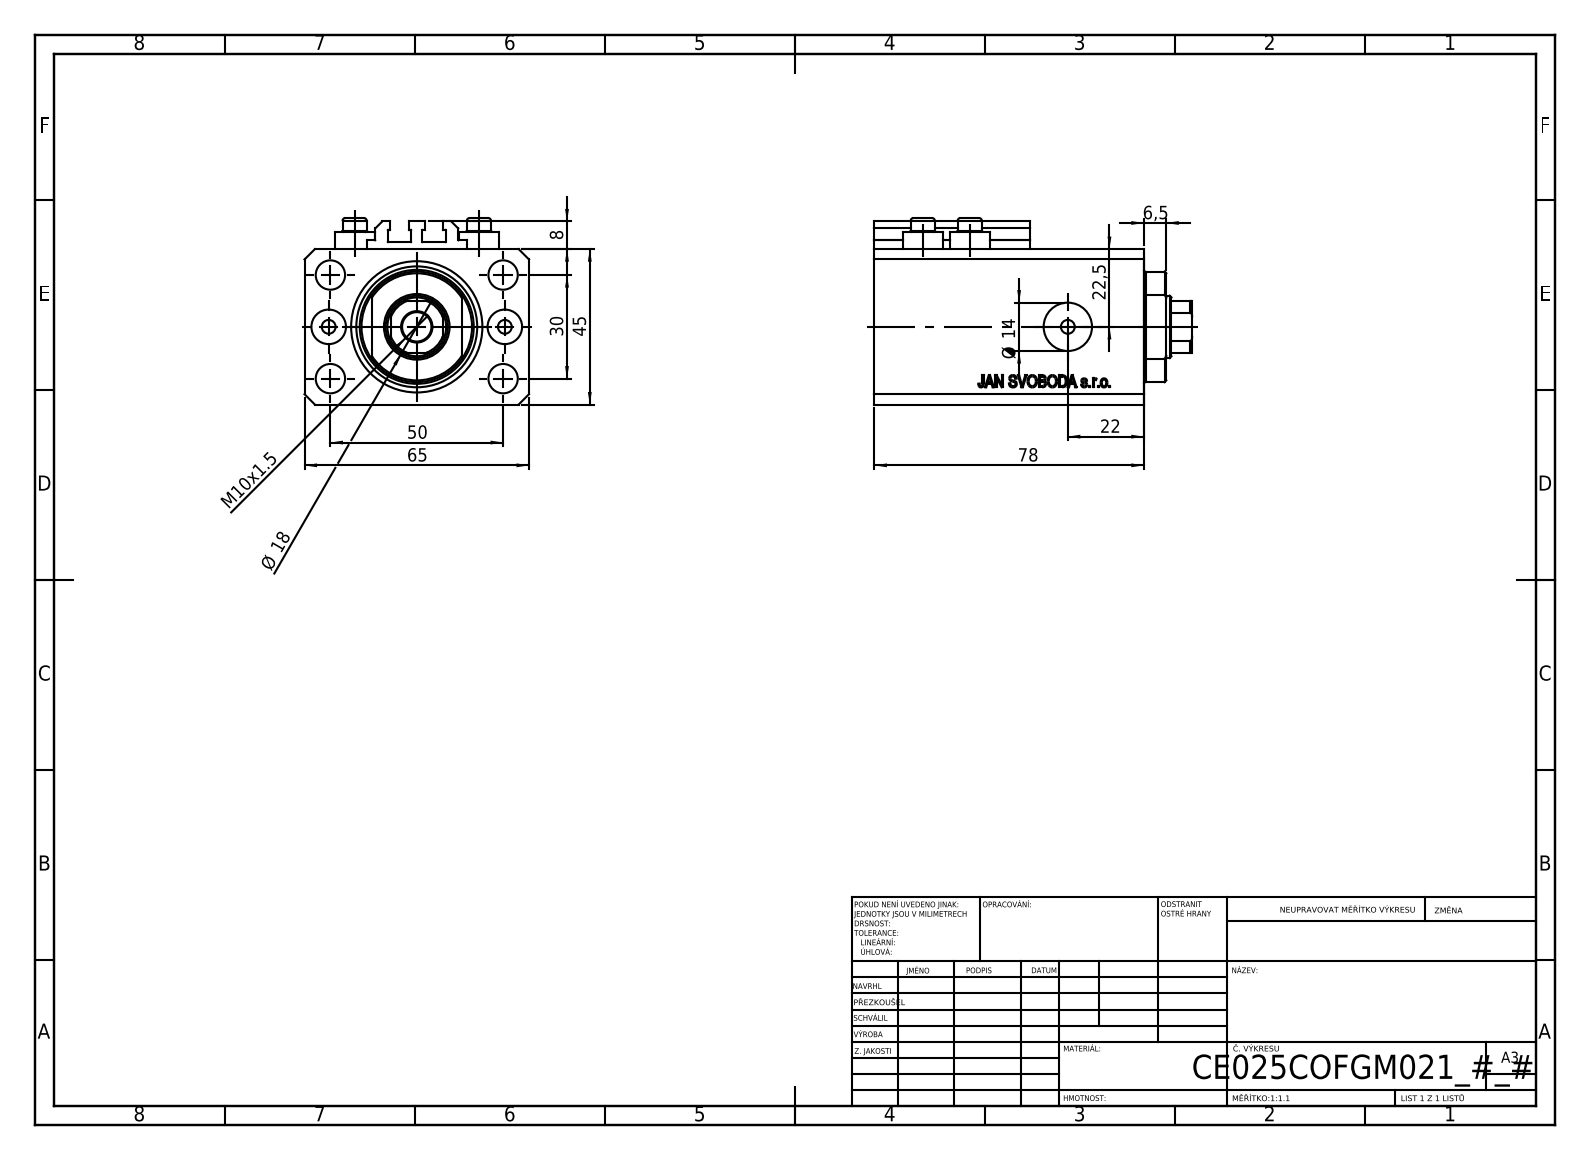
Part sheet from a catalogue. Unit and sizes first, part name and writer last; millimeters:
Units: millimetres
Overall size (bounding box): 92 × 65 × 54
Round holes (diameter × count): ⌀4 ×8, ⌀8.5 ×5, ⌀10 ×2, ⌀14 ×2, ⌀18 ×1, ⌀25 ×1, ⌀38 ×1
Round bosses / shafts (diameter × count): ⌀11.6 ×4, ⌀7 ×4
Partial cylindrical surfaces — rounded edges, fillets, slot ends (radius × count): R0.2 ×10, R8.5 ×1, R16 ×1
Main face-to-face distances: 45, 65, 14, 64, 78, 6.9, 57.1, 71.1, 3, 47
Hole centre spacings: 15.01, 29.15, 52.68, 13.6, 25.5, 30, 36, 38.48
Volume: 214 509 mm³ · Surface area: 57 821 mm²
Bodies: 8 solids, 1034 faces (504 planar, 86 cylindrical, 444 other)
Part name (STEP PRODUCT): V250CE_C_VCP; ALLEN BOLT V250CE; V250CE_VC_C; V250CE_C_Body
STEP written by: SolidWorks 2019 (CONFIG_CONTROL_DESIGN)
